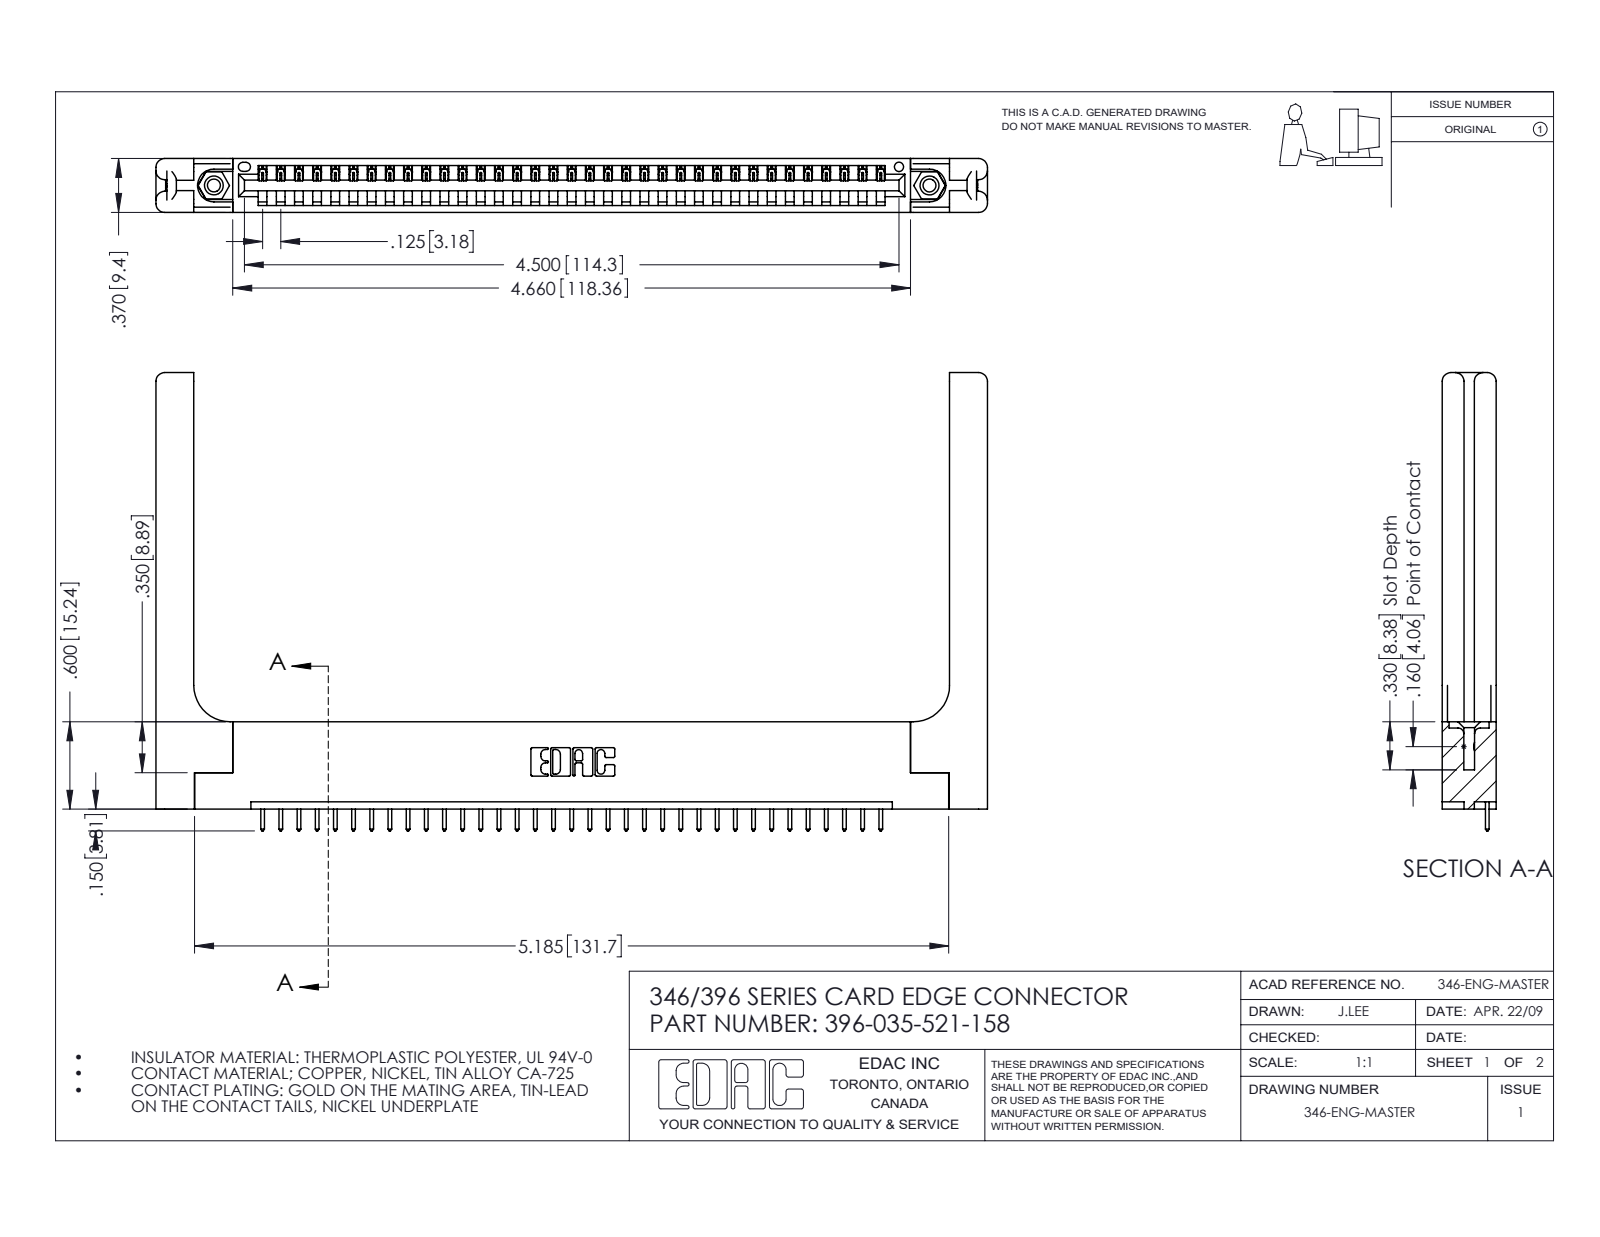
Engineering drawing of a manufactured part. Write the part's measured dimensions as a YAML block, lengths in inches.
part_name: "346-220-058_345-220-058; 345-250-001_345-250-001-102; 396-035-521-158; 345-292-001_345-293-121 (+1 more)"
step_written_by: "SolidWorks 2016 (CONFIG_CONTROL_DESIGN)"
units: inches
bodies: {solids: 40, faces: 2408, planar: 1624, cylindrical: 724, other: 60}
overall_size: [5.716, 3.15, 0.37]
volume: 1.298
surface_area: 33.92
round_holes:
  - {diameter: 0.089, count: 2}
  - {diameter: 0.125, count: 2}
  - {diameter: 0.156, count: 2}
  - {diameter: 0.064, count: 1}
round_bosses_or_shafts:
  - {diameter: 0.155, count: 2}
partial_cylinders:
  - {radius: 0.006, count: 70}
  - {radius: 0.01, count: 70}
  - {radius: 0.01, count: 22}
  - {radius: 0.06, count: 16}
  - {radius: 0.007, count: 6}
  - {radius: 0.031, count: 6}
  - {radius: 0.026, count: 3}
  - {radius: 0.03, count: 2}
face_to_face_distances: [0.37, 0.048, 0.322, 0.072, 0.148, 0.15, 0.25, 0.298, 0.025, 0.222]
hole_center_spacings: [0.246, 4.711, 4.92]
